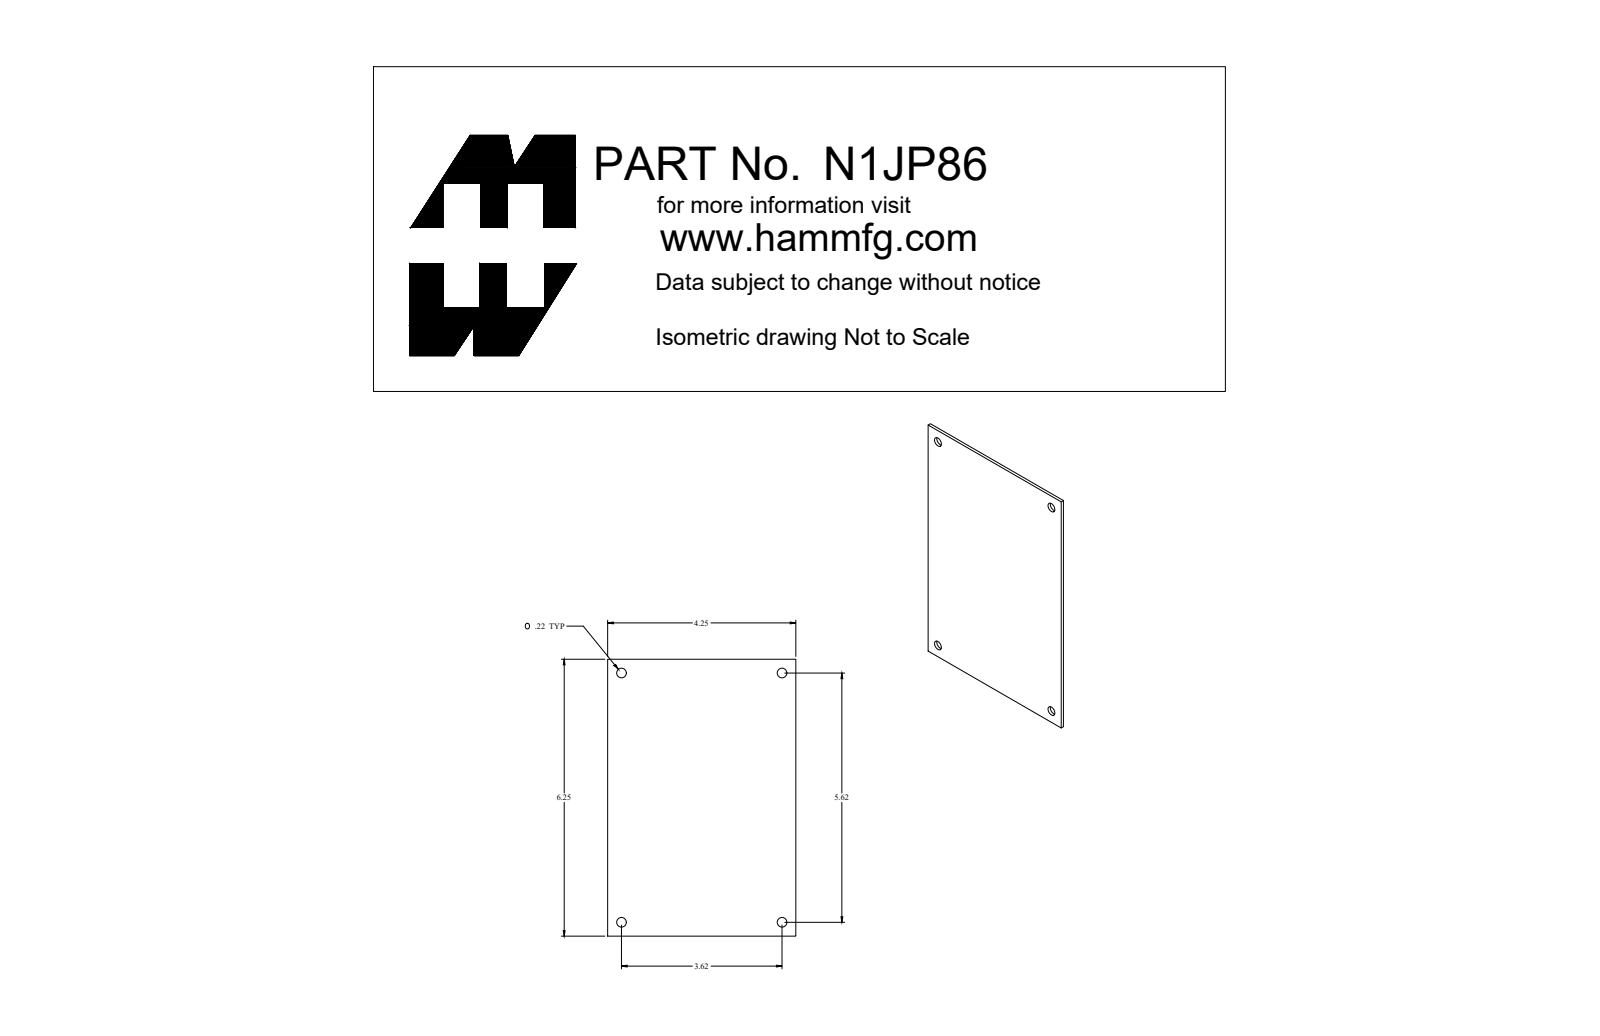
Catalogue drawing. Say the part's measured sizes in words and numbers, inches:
The part is named "N1JP86". Its 3-D file was written by "SolidWorks 2018 (AUTOMOTIVE_DESIGN)". It is 1 solid with 18 faces: 6 planar, 12 cylindrical and 0 other. Overall it measures 6.25 by 4.25 by 0.072 inches. Its volume is 1.896 cubic inches and its surface area 54.39 square inches. Round holes: 4 of diameter 0.265. Partial cylindrical surfaces (rounded edges, fillets, slot ends): 4 of radius 0.125. The main face-to-face distances are 0.072, 4.25, 6.25. The hole center spacings are 3.625, 5.625, 6.692.
